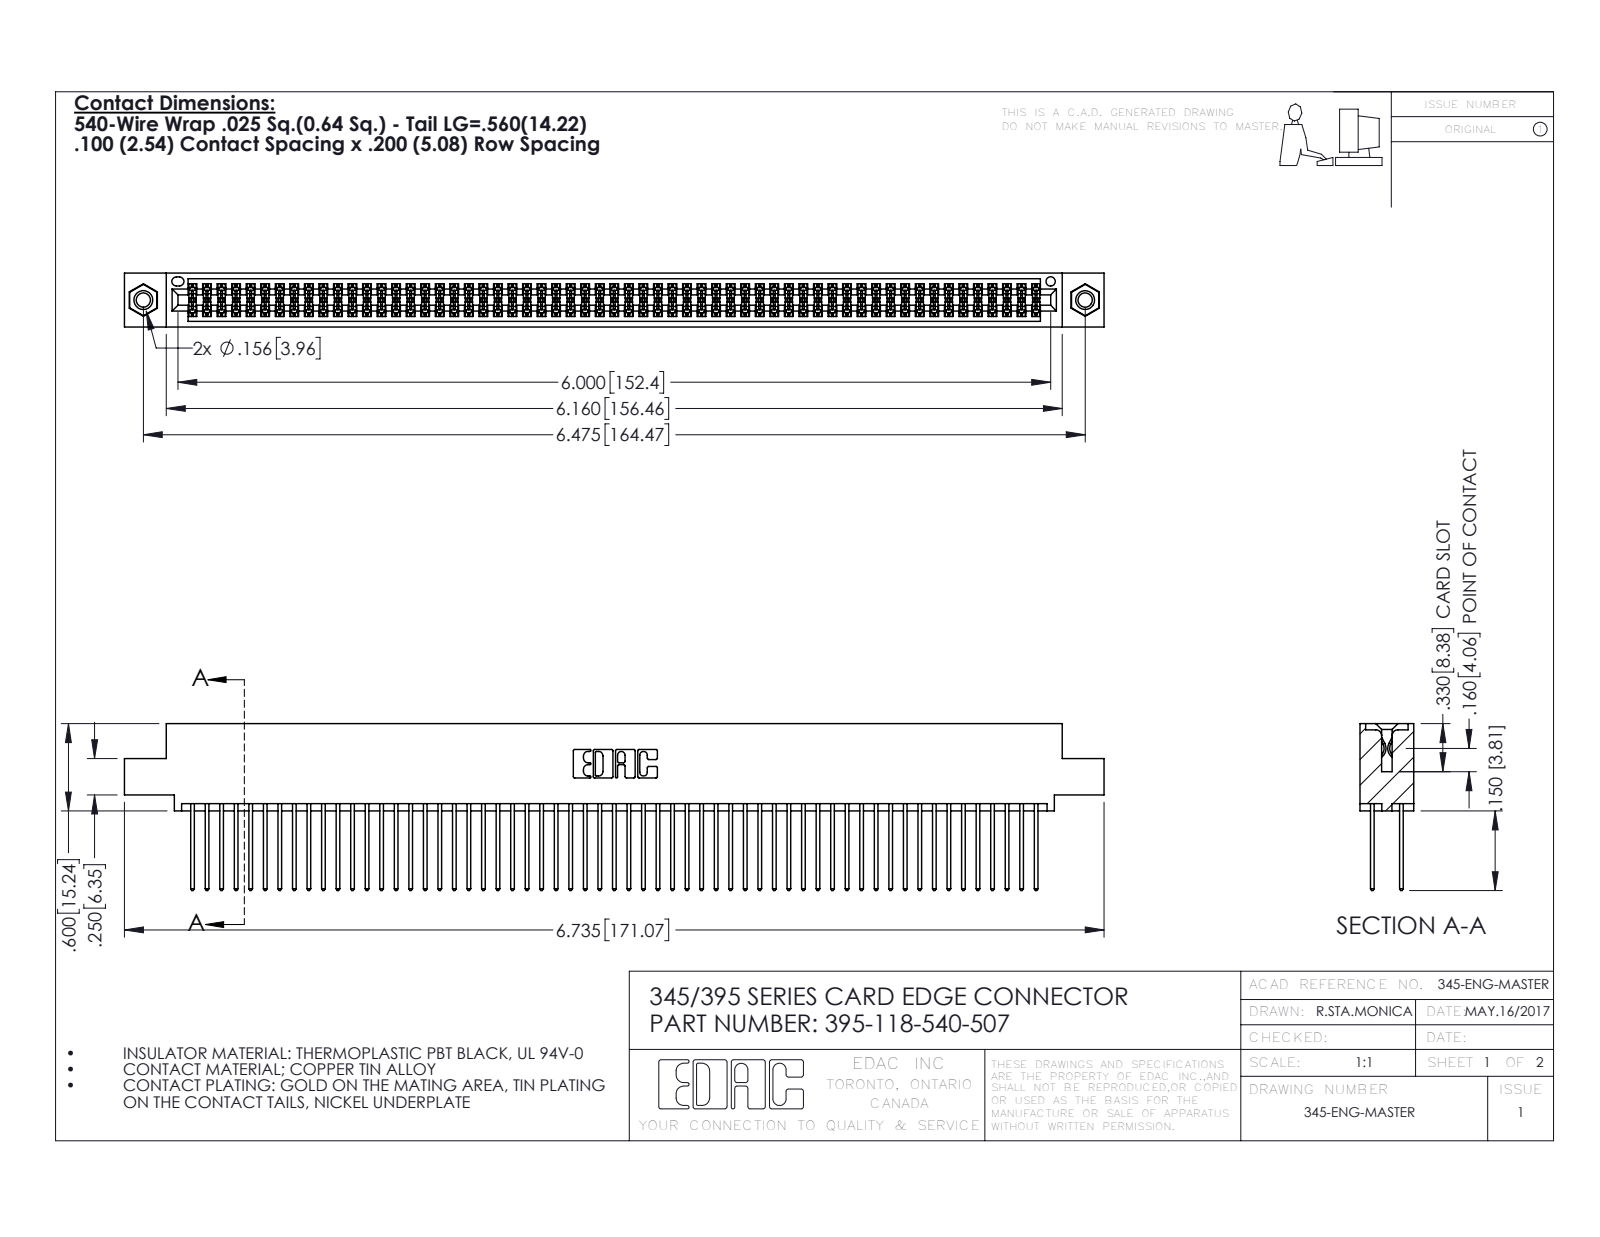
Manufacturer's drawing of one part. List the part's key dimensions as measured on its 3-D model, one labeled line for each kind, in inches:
Part name (STEP PRODUCT): 395-118-540-507; 345-250-001_345-250-005-103; 345-292-001_345-293-140; 345 Part_0.110 Offset - 0.156 Dia-TI
STEP written by: SolidWorks 2016 (CONFIG_CONTROL_DESIGN)
Units: inches
Bodies: 121 solids, 6090 faces (4010 planar, 2064 cylindrical, 16 other)
Overall size (bounding box): 6.735 × 1.147 × 0.37
Volume: 1.046 in³ · Surface area: 43.18 in²
Round holes (diameter × count): ⌀0.098 ×2, ⌀0.125 ×2, ⌀0.156 ×2, ⌀0.064 ×1
Round bosses / shafts (diameter × count): ⌀0.155 ×2
Partial cylindrical surfaces — rounded edges, fillets, slot ends (radius × count): R0.006 ×177, R0.01 ×118, R0.01 ×22, R0.007 ×6, R0.031 ×6, R0.026 ×3, R0.014 ×2, R0.019 ×2
Main face-to-face distances: 0.072, 0.298, 0.2, 0.098, 0.272, 0.025, 0.37, 0.225, 0.175, 0.149
Hole centre spacings: 0.27, 6.239, 6.475
